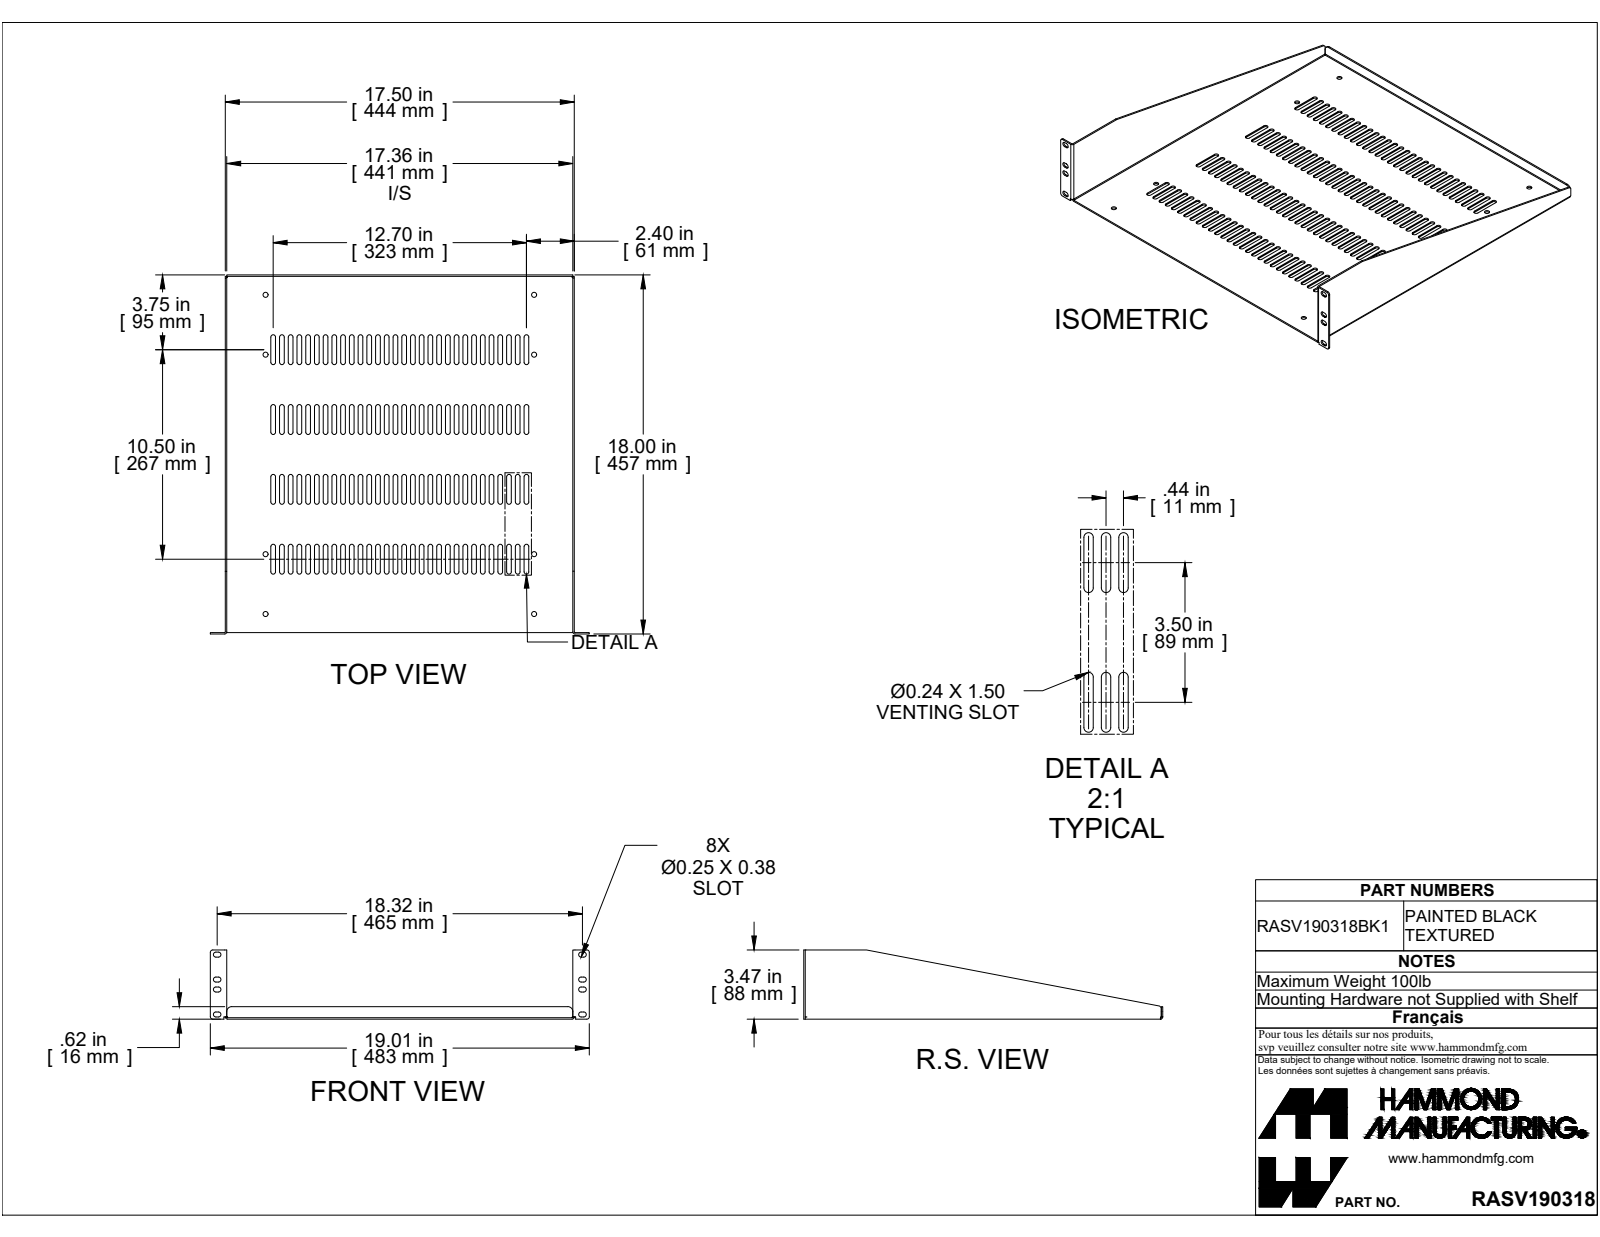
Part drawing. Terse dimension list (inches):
name: RASV190318BK1
written by: SolidWorks 2019 (CONFIG_CONTROL_DESIGN)
unit: in
bodies: 1 solid, 584 faces (296 planar, 284 cylindrical, 4 other)
size: 19.006 × 18 × 3.468
volume: 26.26 in³; area: 764.6 in²
holes: 8× ⌀0.25
rounds: 232× R0.118, 20× R0.125, 8× R0.117, 5× R0.036, 5× R0.108, 3× R0.055, 2× R0.25
face distances: 0.072, 17.428, 17.356, 17.5, 17.856, 17.928, 0.876, 0.072, 17.928, 18
hole spacings: 3, 13, 13.468, 13.798, 18.719, 10, 16, 16.774
